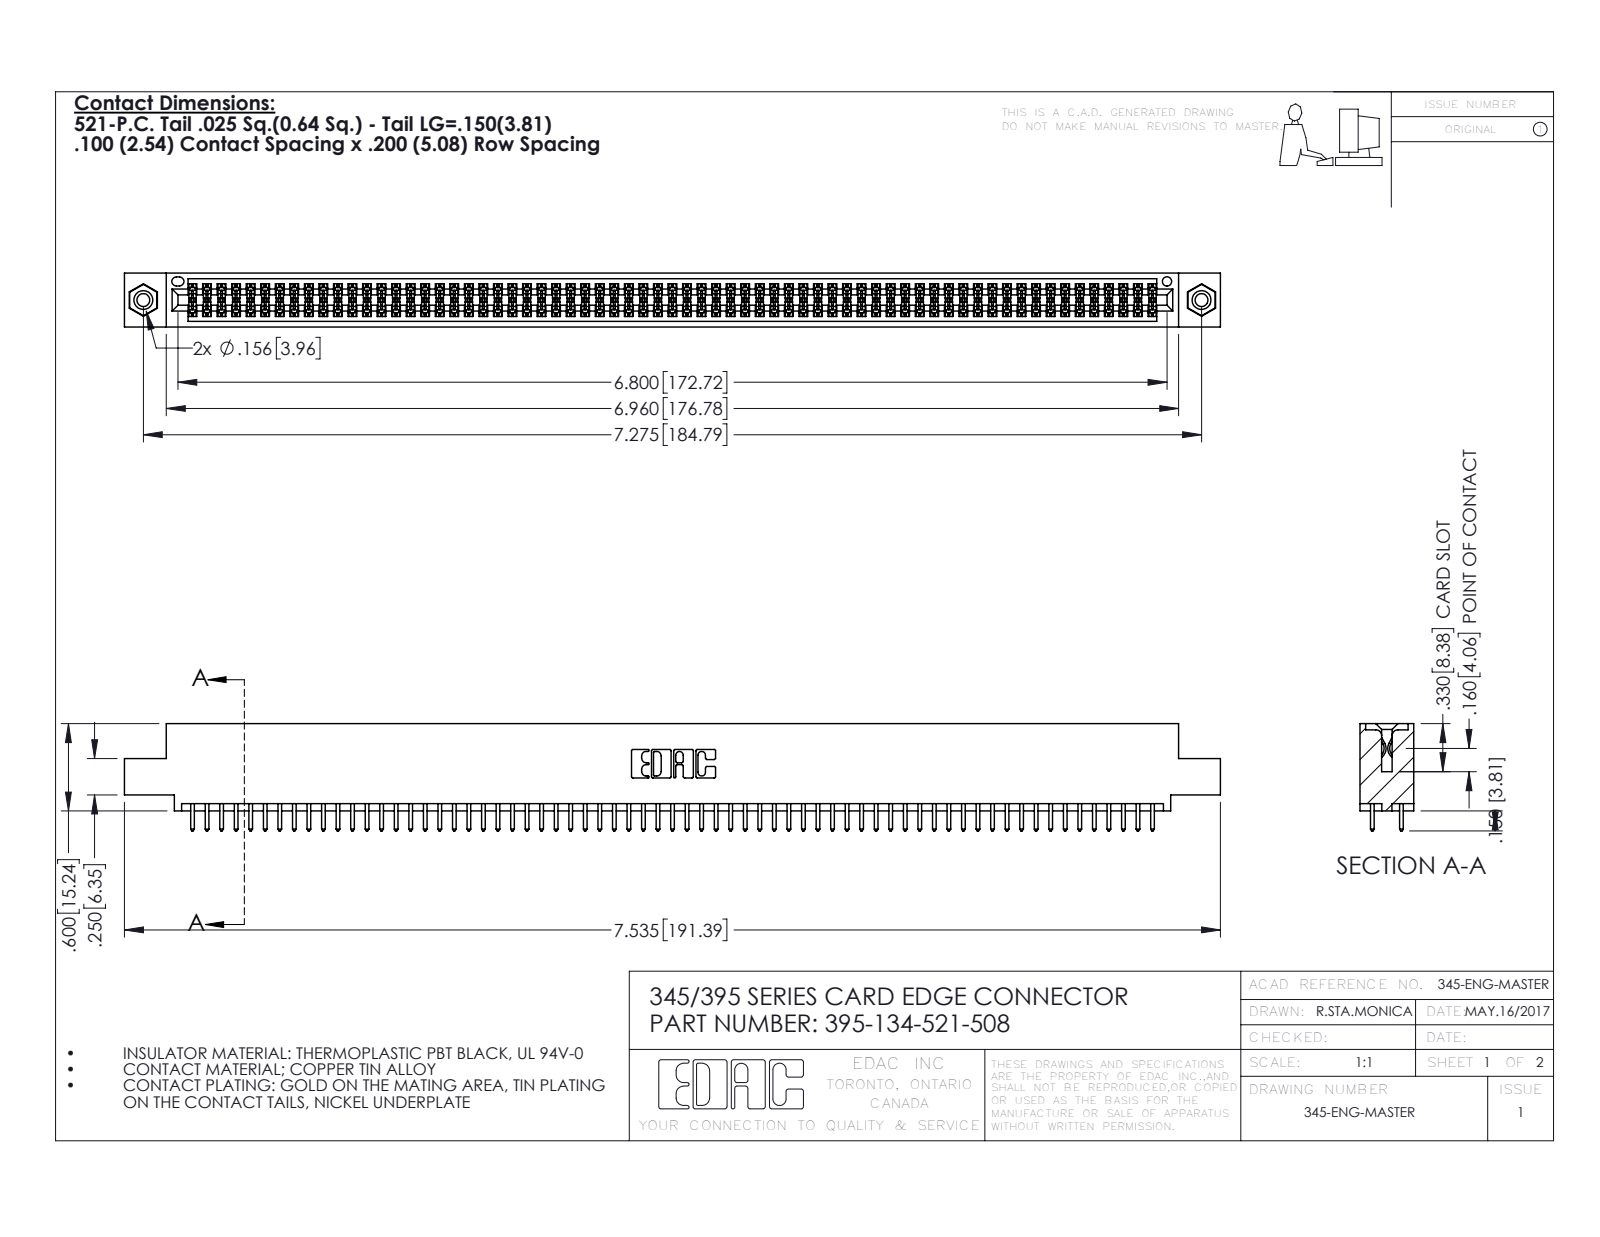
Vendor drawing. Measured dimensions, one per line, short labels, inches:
name: 345-250-001_345-250-003-102; 345 Part_0.110 Offset - 0.156 Dia-TI; 345-292-001_345-293-121; 395-134-521-508
written by: SolidWorks 2016 (CONFIG_CONTROL_DESIGN)
unit: in
bodies: 137 solids, 6890 faces (4538 planar, 2336 cylindrical, 16 other)
size: 7.535 × 0.737 × 0.37
volume: 1.14 in³; area: 43.18 in²
holes: 2× ⌀0.089, 2× ⌀0.125, 2× ⌀0.156, 1× ⌀0.064
bosses: 2× ⌀0.155
rounds: 201× R0.006, 134× R0.01, 22× R0.01, 6× R0.007, 6× R0.031, 3× R0.026, 2× R0.014, 2× R0.019
face distances: 0.072, 0.298, 0.2, 0.098, 0.272, 0.025, 0.37, 0.225, 0.175, 0.149
hole spacings: 0.27, 7.039, 7.275
